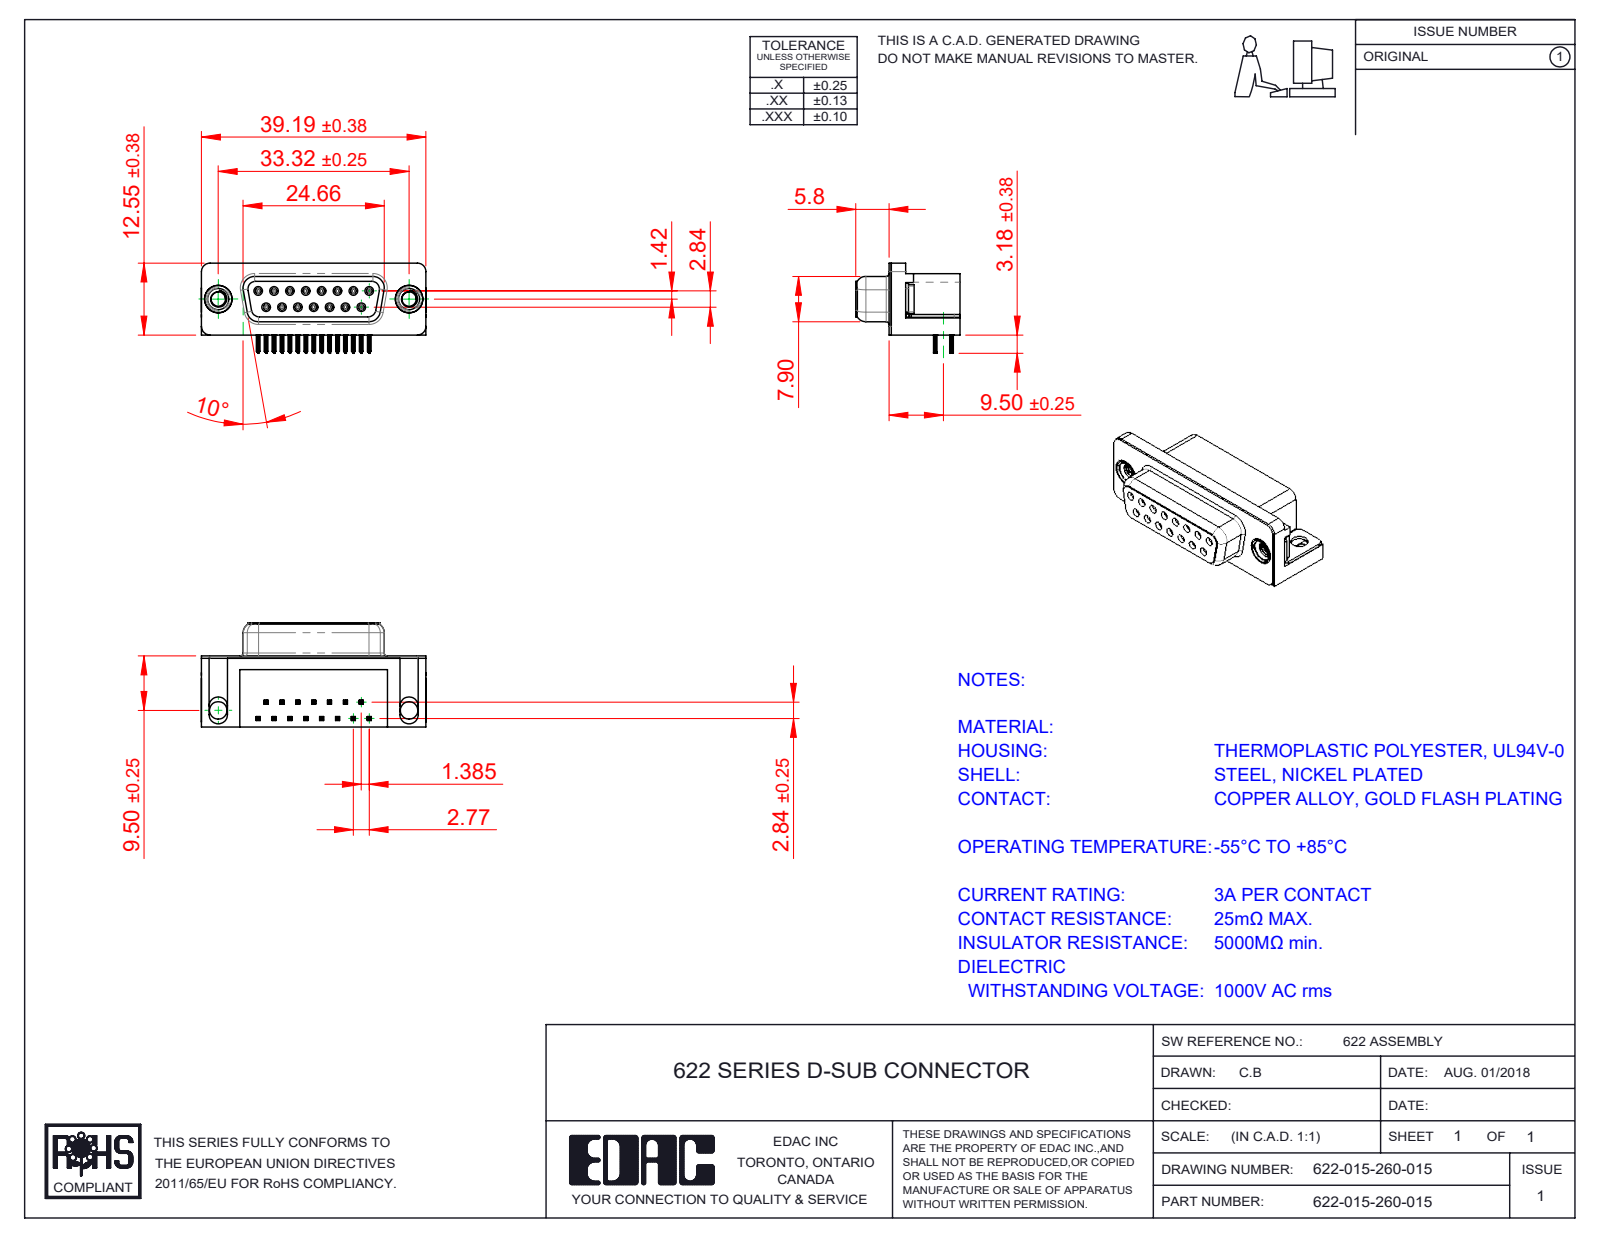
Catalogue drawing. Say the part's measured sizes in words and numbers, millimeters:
The part is named "622 Thru Hole Board Mount; 622 M3 Threaded Rivet; 622 Socket Bottom; 622 Housing_15 Socket (+3 more)". Its 3-D file was written by "SolidWorks 2016 (CONFIG_CONTROL_DESIGN)". It is 21 solids with 2425 faces: 1072 planar, 609 cylindrical and 744 other. Overall it measures 39.22 by 18.2 by 15.73 millimeters. Its volume is 5 181 cubic millimeters and its surface area 6 706 square millimeters. Round holes: 15 of diameter 0.8, 15 of diameter 0.9, 2 of diameter 2.5, 2 of diameter 3.05, 2 of diameter 4, 2 of diameter 4.8, 2 of diameter 5. Round bosses or shafts: 15 of diameter 1.2, 2 of diameter 4.9, 2 of diameter 4.75, 2 of diameter 3.9. Partial cylindrical surfaces (rounded edges, fillets, slot ends): 120 of radius 0.1, 60 of radius 0.15, 30 of radius 0.35, 18 of radius 1, 15 of radius 0.34, 8 of radius 0.25, 8 of radius 1.35, 8 of radius 1.5. The main face-to-face distances are 0.4, 12, 6.2, 12.4, 10.35, 2.9, 6.65, 0.85, 0.35, 5.8. The hole center spacings are 3.16, 2.77, 5.54, 8.31, 11.08, 5.03, 5.04, 7.48.
